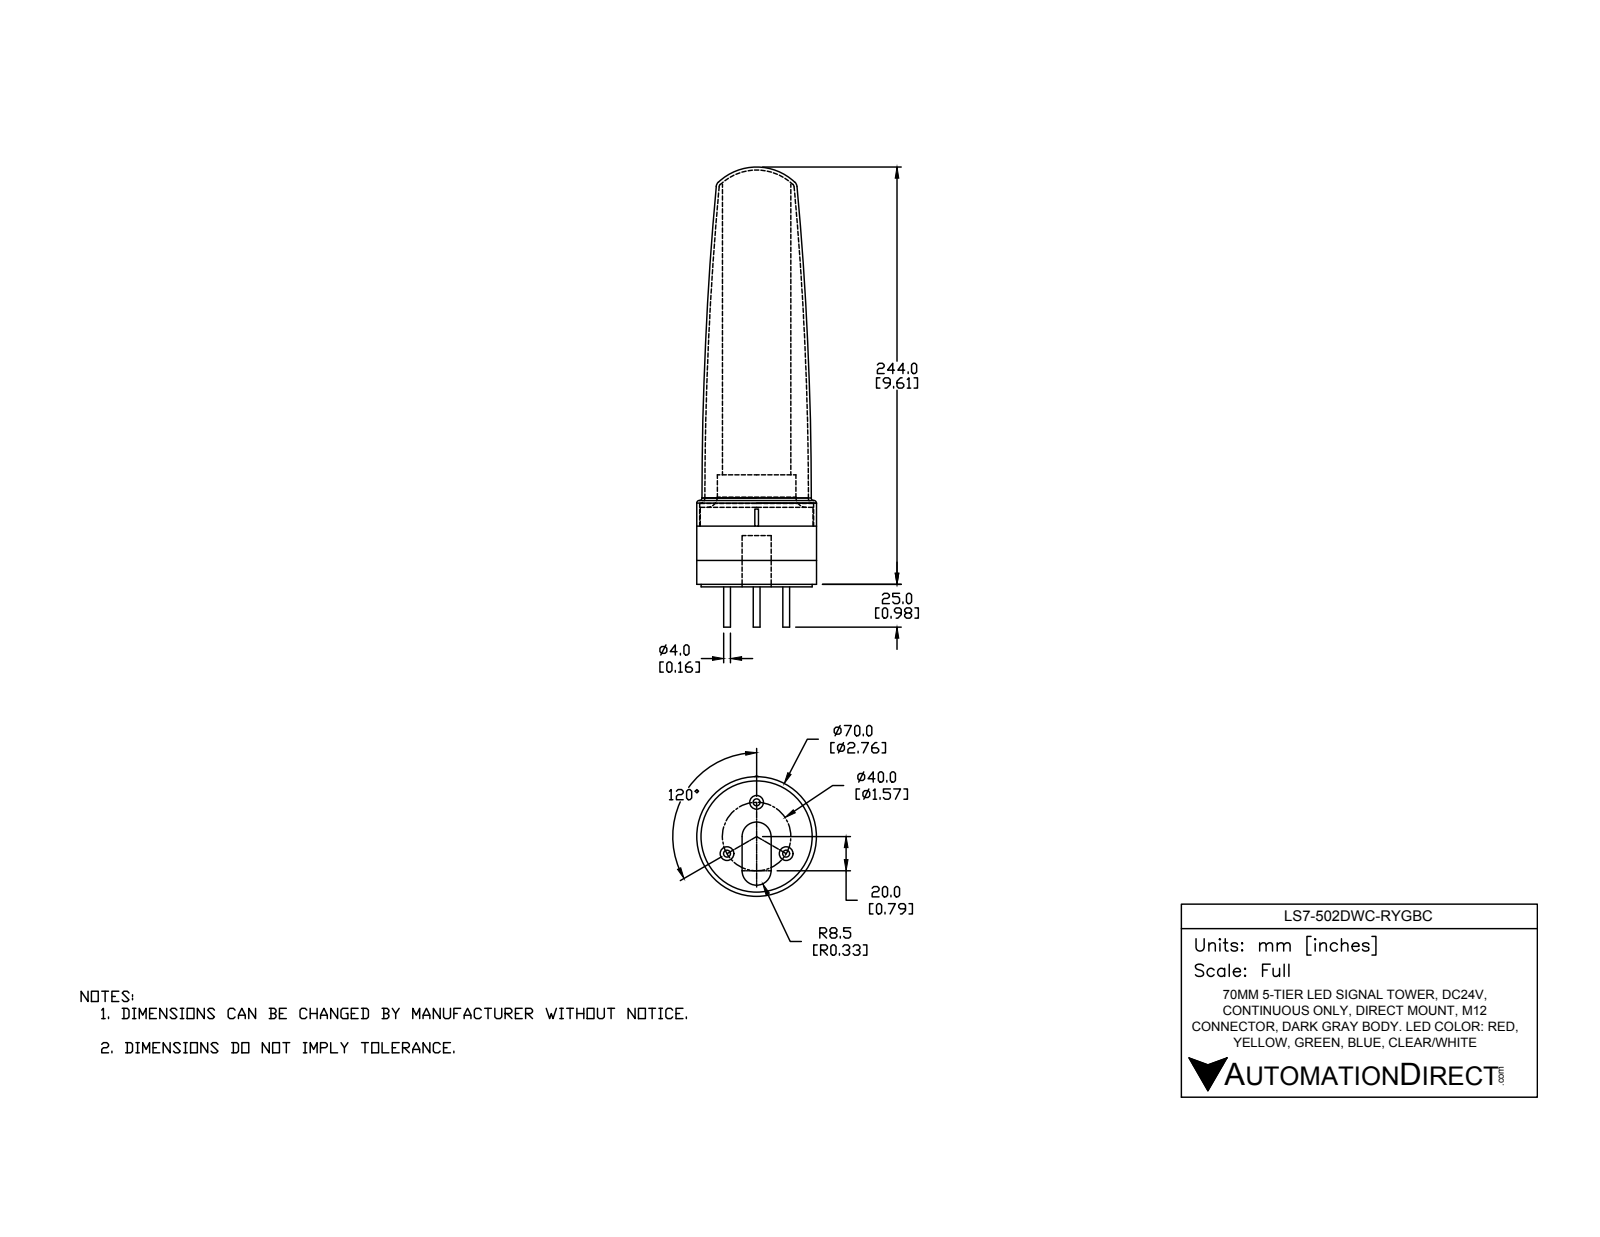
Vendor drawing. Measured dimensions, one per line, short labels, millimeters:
name: LS7-502DWC-RYGBC
written by: SolidWorks 2016 (AUTOMOTIVE_DESIGN)
unit: mm
bodies: 8 solids, 84 faces (27 planar, 39 cylindrical, 18 other)
size: 269 × 70.3 × 70
volume: 468 745 mm³; area: 136 804 mm²
holes: 3× ⌀8, 1× ⌀66.6
bosses: 3× ⌀4, 1× ⌀70, 1× ⌀66, 1× ⌀65, 1× ⌀46, 1× ⌀40
rounds: 2× R8.5, 1× R1, 1× R2
face distances: 14, 64, 50, 15.5, 1.5, 65.5, 30, 35.5, 235.5, 234
hole spacings: 20, 34.64
